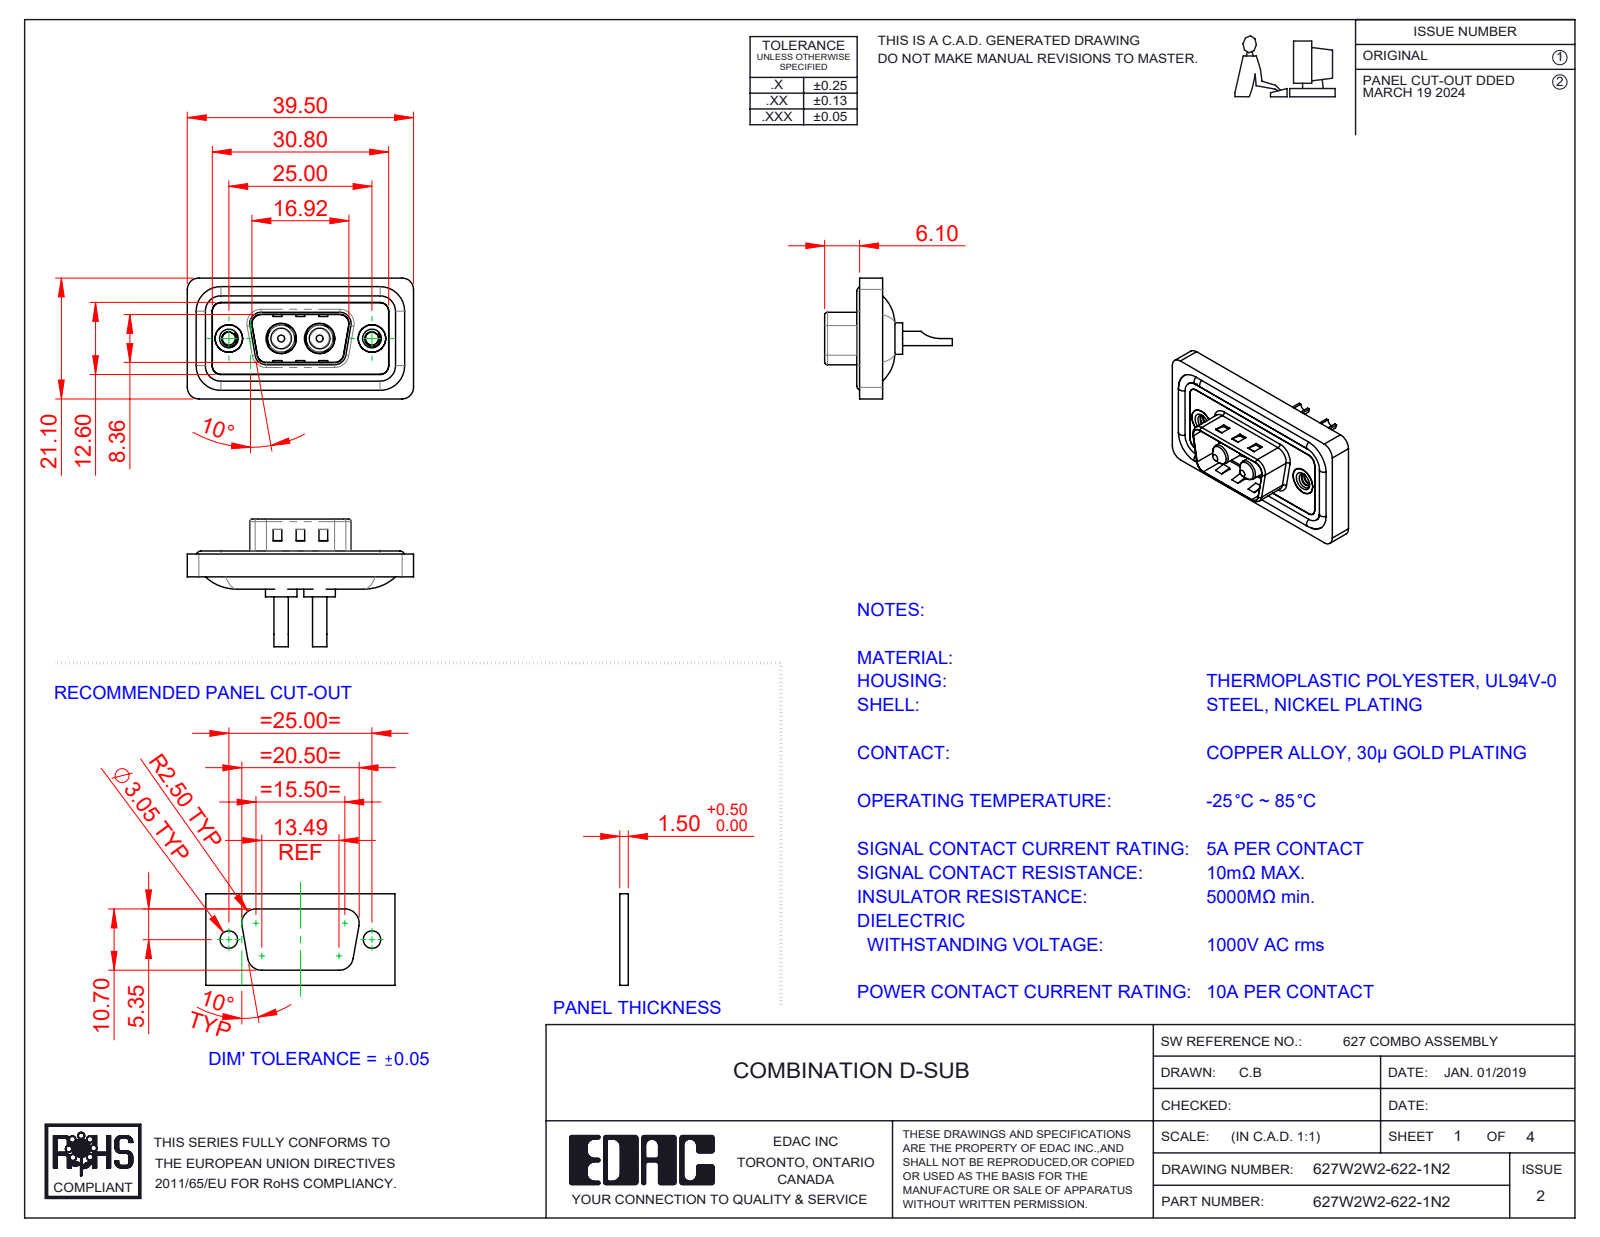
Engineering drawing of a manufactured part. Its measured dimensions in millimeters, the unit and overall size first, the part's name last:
Units: millimetres
Overall size (bounding box): 39.5 × 22.3 × 21.1
Round holes (diameter × count): ⌀1.7 ×2, ⌀2.26 ×2, ⌀4 ×2, ⌀4.8 ×2, ⌀4.85 ×2, ⌀5 ×2, ⌀5.3 ×2
Round bosses / shafts (diameter × count): ⌀1.6 ×4, ⌀5.5 ×2, ⌀5.2 ×2, ⌀4.9 ×2, ⌀4.75 ×2, ⌀3.75 ×2, ⌀3.6 ×2, ⌀2.5 ×2
Partial cylindrical surfaces — rounded edges, fillets, slot ends (radius × count): R1.5 ×22, R2 ×18, R0.5 ×8, R1.6 ×8, R0.25 ×4, R0.6 ×4, R0.65 ×4, R0.9 ×4
Main face-to-face distances: 0.4, 1.1, 2.9, 3.1, 0.5, 1.5, 1.6, 4, 2.5, 0.7
Hole centre spacings: 9.14, 15.86, 6.72, 25
Volume: 4 455 mm³ · Surface area: 7 079 mm²
Bodies: 11 solids, 501 faces (169 planar, 224 cylindrical, 108 other)
Part name (STEP PRODUCT): Power Pin_10A SC; 627W2W2-622-1N2; 627Combo Threaded Rivet_2; 627Combo Shell Rear_09 Contacts (+3 more)
STEP written by: SolidWorks 2023 (CONFIG_CONTROL_DESIGN)
